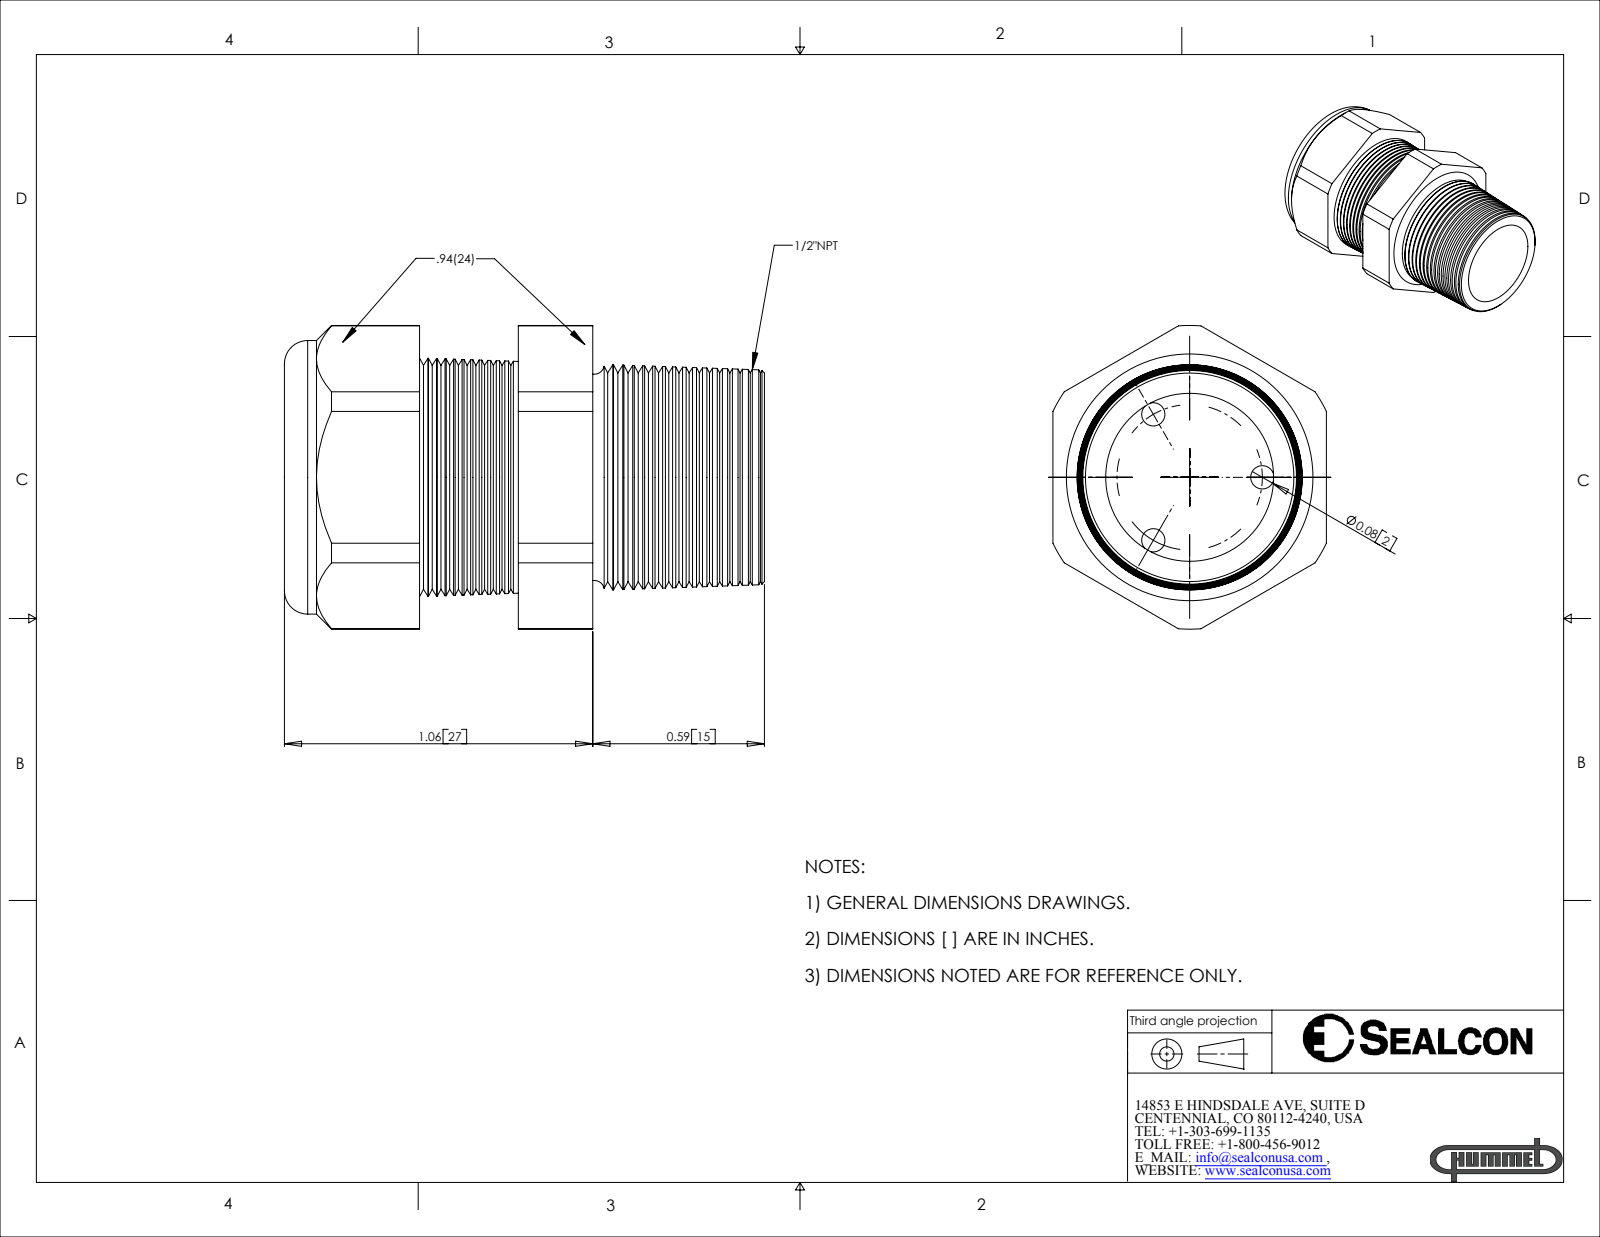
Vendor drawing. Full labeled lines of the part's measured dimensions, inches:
Part name (STEP PRODUCT): CD13N1-GY
STEP written by: SolidWorks 2007 (CONFIG_CONTROL_DESIGN)
Units: inches
Bodies: 2 solids, 210 faces (20 planar, 26 cylindrical, 164 other)
Overall size (bounding box): 1.57 × 1.043 × 0.94
Volume: 0.573 in³ · Surface area: 11.54 in²
Round holes (diameter × count): ⌀0.08 ×3, ⌀0.58 ×1, ⌀0.6 ×1
Round bosses / shafts (diameter × count): ⌀0.94 ×1
Partial cylindrical surfaces — rounded edges, fillets, slot ends (radius × count): R0.522 ×1
Main face-to-face distances: 0.94, 0.454, 0.33, 0.784, 0.444, 0.115, 0.34, 0.02, 0.35, 0.465
Hole centre spacings: 0.25, 0.433, 0.433
